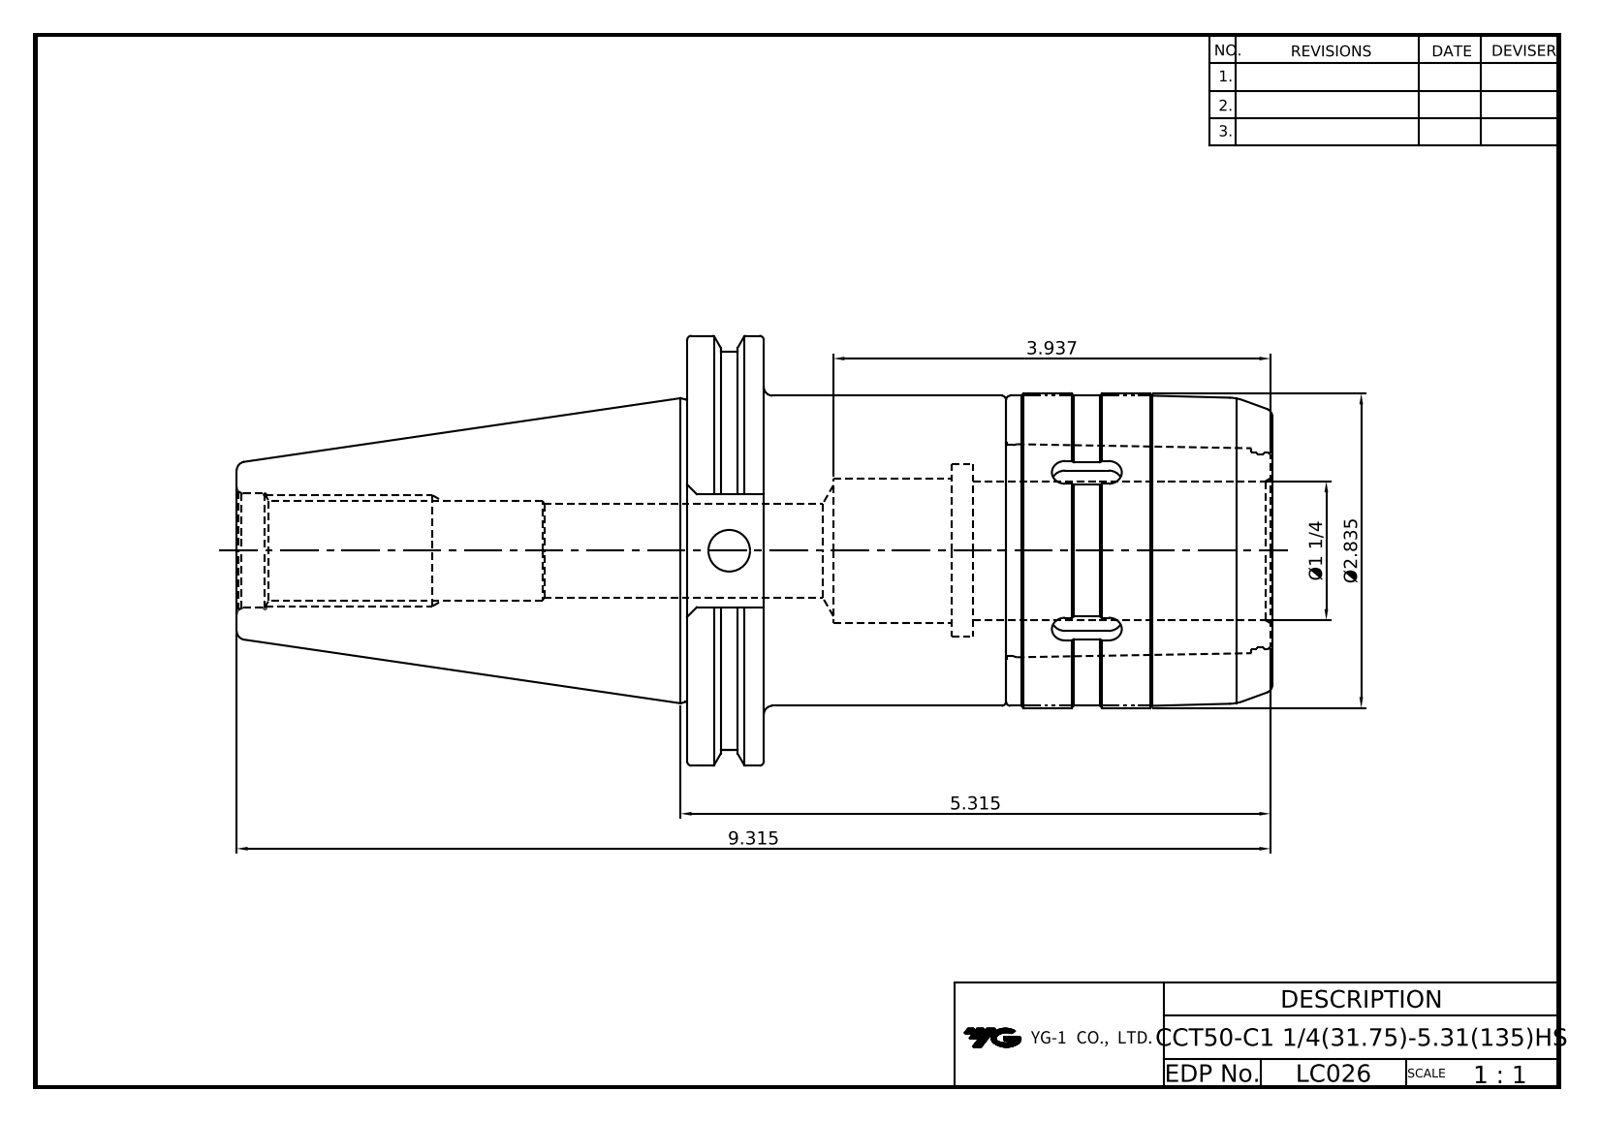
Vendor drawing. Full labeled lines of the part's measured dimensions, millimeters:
Part name (STEP PRODUCT): LO-CCT50-C31.75-135; C32-CAP
STEP written by: Autodesk Inventor 2022 (AUTOMOTIVE_DESIGN)
Units: millimetres
Bodies: 2 solids, 178 faces (78 planar, 43 cylindrical, 57 other)
Overall size (bounding box): 237.1 × 98.42 × 94.69
Volume: 671 167 mm³ · Surface area: 105 334 mm²
Round holes (diameter × count): ⌀9.53 ×1, ⌀21 ×1, ⌀21.97 ×1, ⌀26.2 ×1, ⌀31.75 ×1, ⌀33 ×1, ⌀39.5 ×1, ⌀56 ×1, ⌀58 ×1
Round bosses / shafts (diameter × count): ⌀98.42 ×1, ⌀91.29 ×1, ⌀72 ×1, ⌀71 ×1, ⌀69.25 ×1, ⌀45 ×1
Partial cylindrical surfaces — rounded edges, fillets, slot ends (radius × count): R3 ×6, R12.95 ×1
Main face-to-face distances: 73, 55.45, 17.55, 60.5, 134, 116.45, 61, 133.5, 115.95, 0.5
